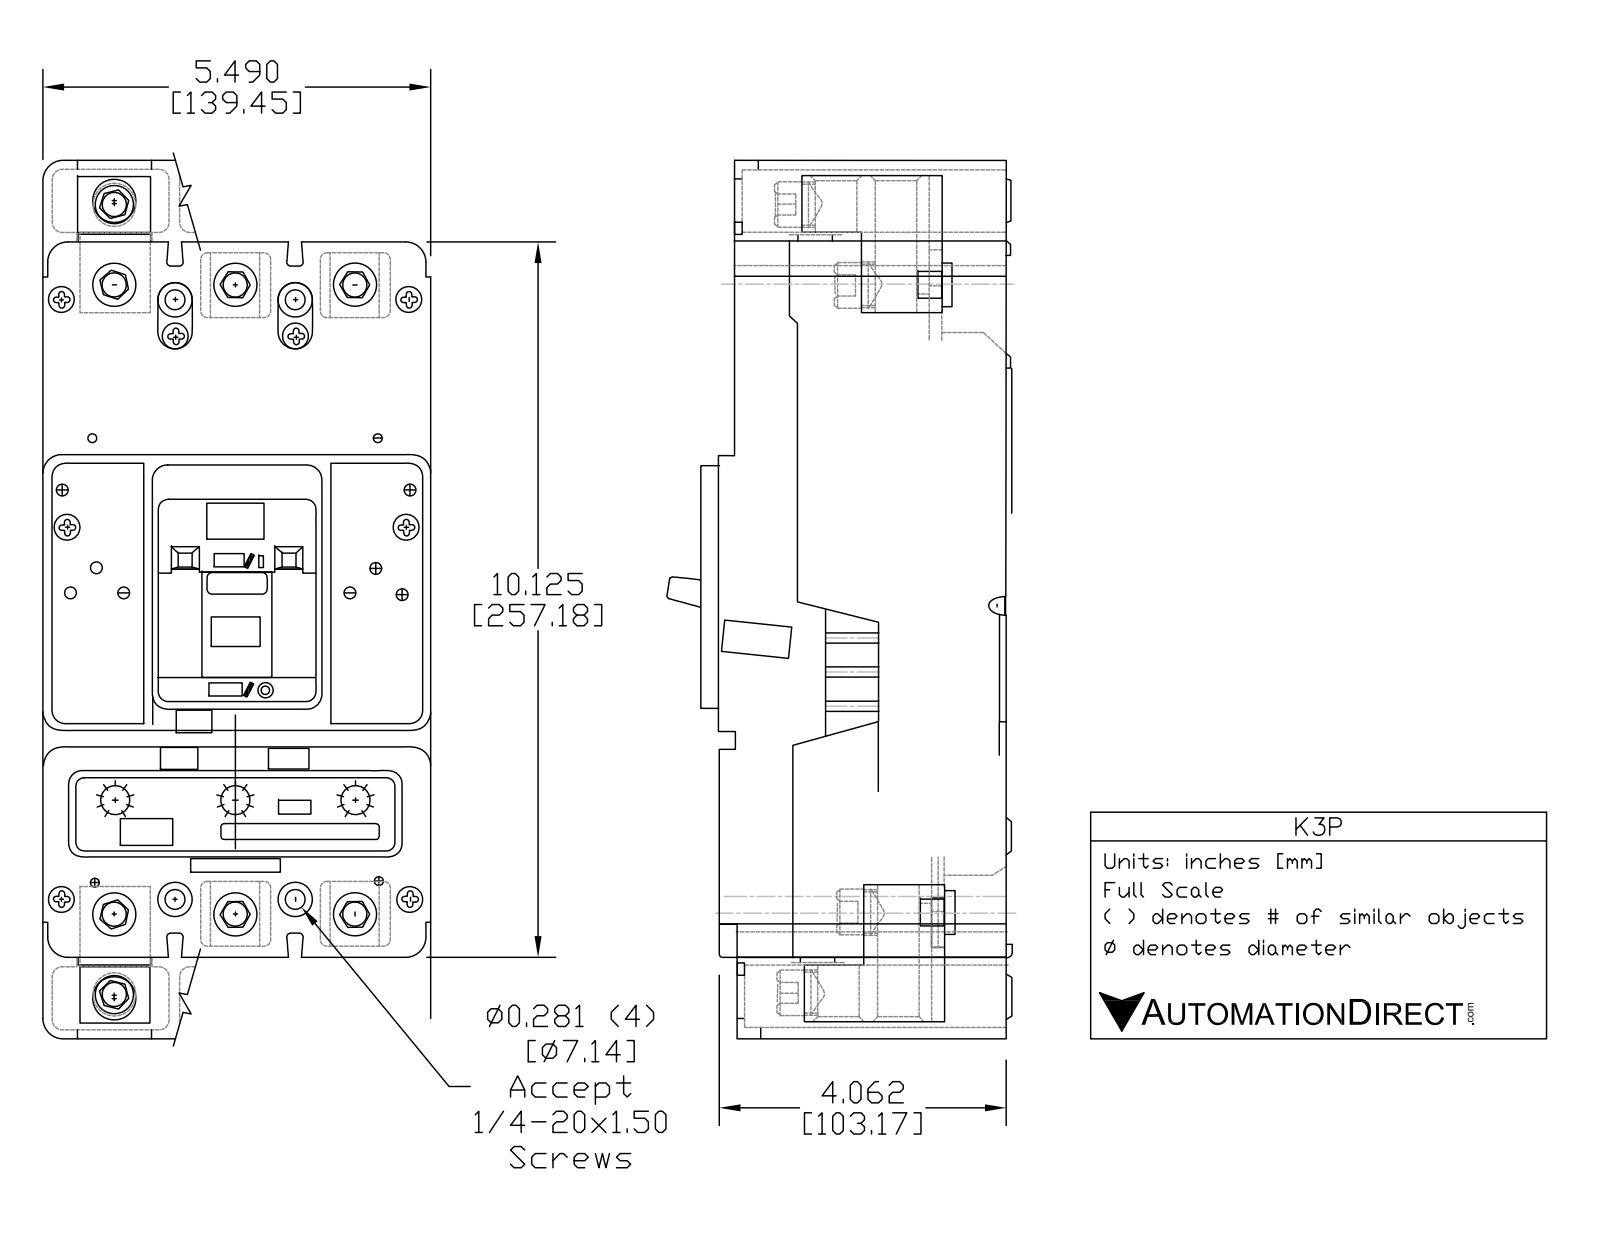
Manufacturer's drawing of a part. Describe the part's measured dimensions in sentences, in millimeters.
The part is named "K3P-250". Its 3-D file was written by "SolidWorks 2013 (AUTOMOTIVE_DESIGN)". It is 56 solids with 1374 faces: 956 planar, 327 cylindrical and 91 other. Overall it measures 316.14 by 139.43 by 122.17 millimeters. Its volume is 3 548 000 cubic millimeters and its surface area 560 289 square millimeters. Round holes: 6 of diameter 12.34, 6 of diameter 15.52, 4 of diameter 2.9, 4 of diameter 7, 3 of diameter 3.18, 3 of diameter 6, 3 of diameter 9.28, 3 of diameter 10.44, 3 of diameter 15.52, 3 of diameter 15.75, 2 of diameter 7.8, 1 of diameter 3.18. Round bosses or shafts: 12 of diameter 15, 3 of diameter 20. Partial cylindrical surfaces (rounded edges, fillets, slot ends): 24 of radius 2, 24 of radius 3, 16 of radius 1.5, 14 of radius 4, 12 of radius 6, 12 of radius 7, 6 of radius 10, 4 of radius 1.44. The main face-to-face distances are 2, 72.75, 1.5, 27, 74.25, 29.48, 286.66, 25.5, 43.22, 22.75. The hole center spacings are 43.68, 237.38, 16.08, 42.69, 43.38, 46.38, 221.36, 221.39.
